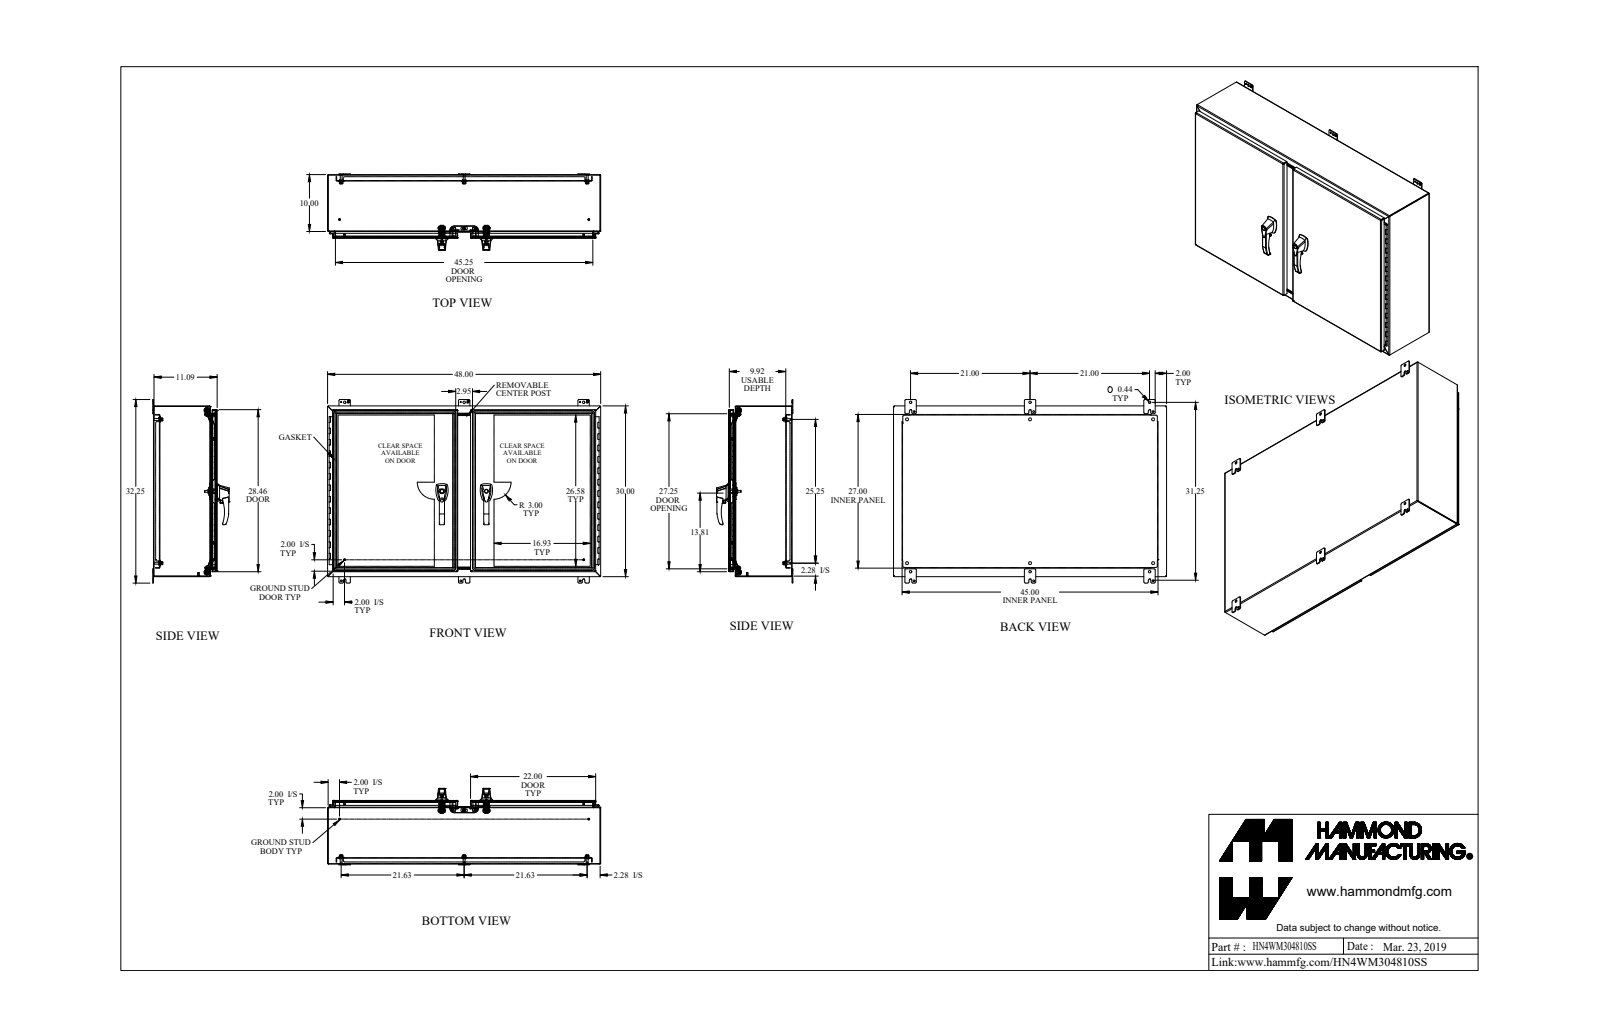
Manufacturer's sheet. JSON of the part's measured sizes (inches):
{"part_name": "HN4WM304810SS", "step_written_by": "SolidWorks 2018 (AUTOMOTIVE_DESIGN)", "units": "inches", "bodies": {"solids": 102, "faces": 2772, "planar": 1305, "cylindrical": 1187, "other": 280}, "overall_size": [48, 32.25, 13.425], "volume_in3": 667.5, "surface_area_in2": 13803, "round_holes": [[0.304, 10], [0.313, 9], [0.25, 8], [0.201, 6], [0.307, 6], [0.445, 6], [0.5, 6], [0.281, 4], [0.313, 4], [0.39, 4], [0.437, 3], [0.11, 2]], "round_bosses_or_shafts": [[1, 8], [0.65, 6], [0.375, 6], [0.332, 6], [0.293, 6], [0.75, 4], [0.625, 4], [0.44, 4]], "partial_cylinders_radius": [[0.125, 37], [0.25, 34], [0.018, 32], [0.188, 26], [0.06, 22], [0.5, 21], [0.048, 19], [0.143, 19]], "face_to_face_distances": [0.095, 1.032, 0.095, 11.09, 10.995, 0.937, 11.185, 11.09, 9.963, 1.127], "hole_center_spacings": [21.625, 6, 46.53, 33.245, 12, 21.625, 25.25, 33.244]}
